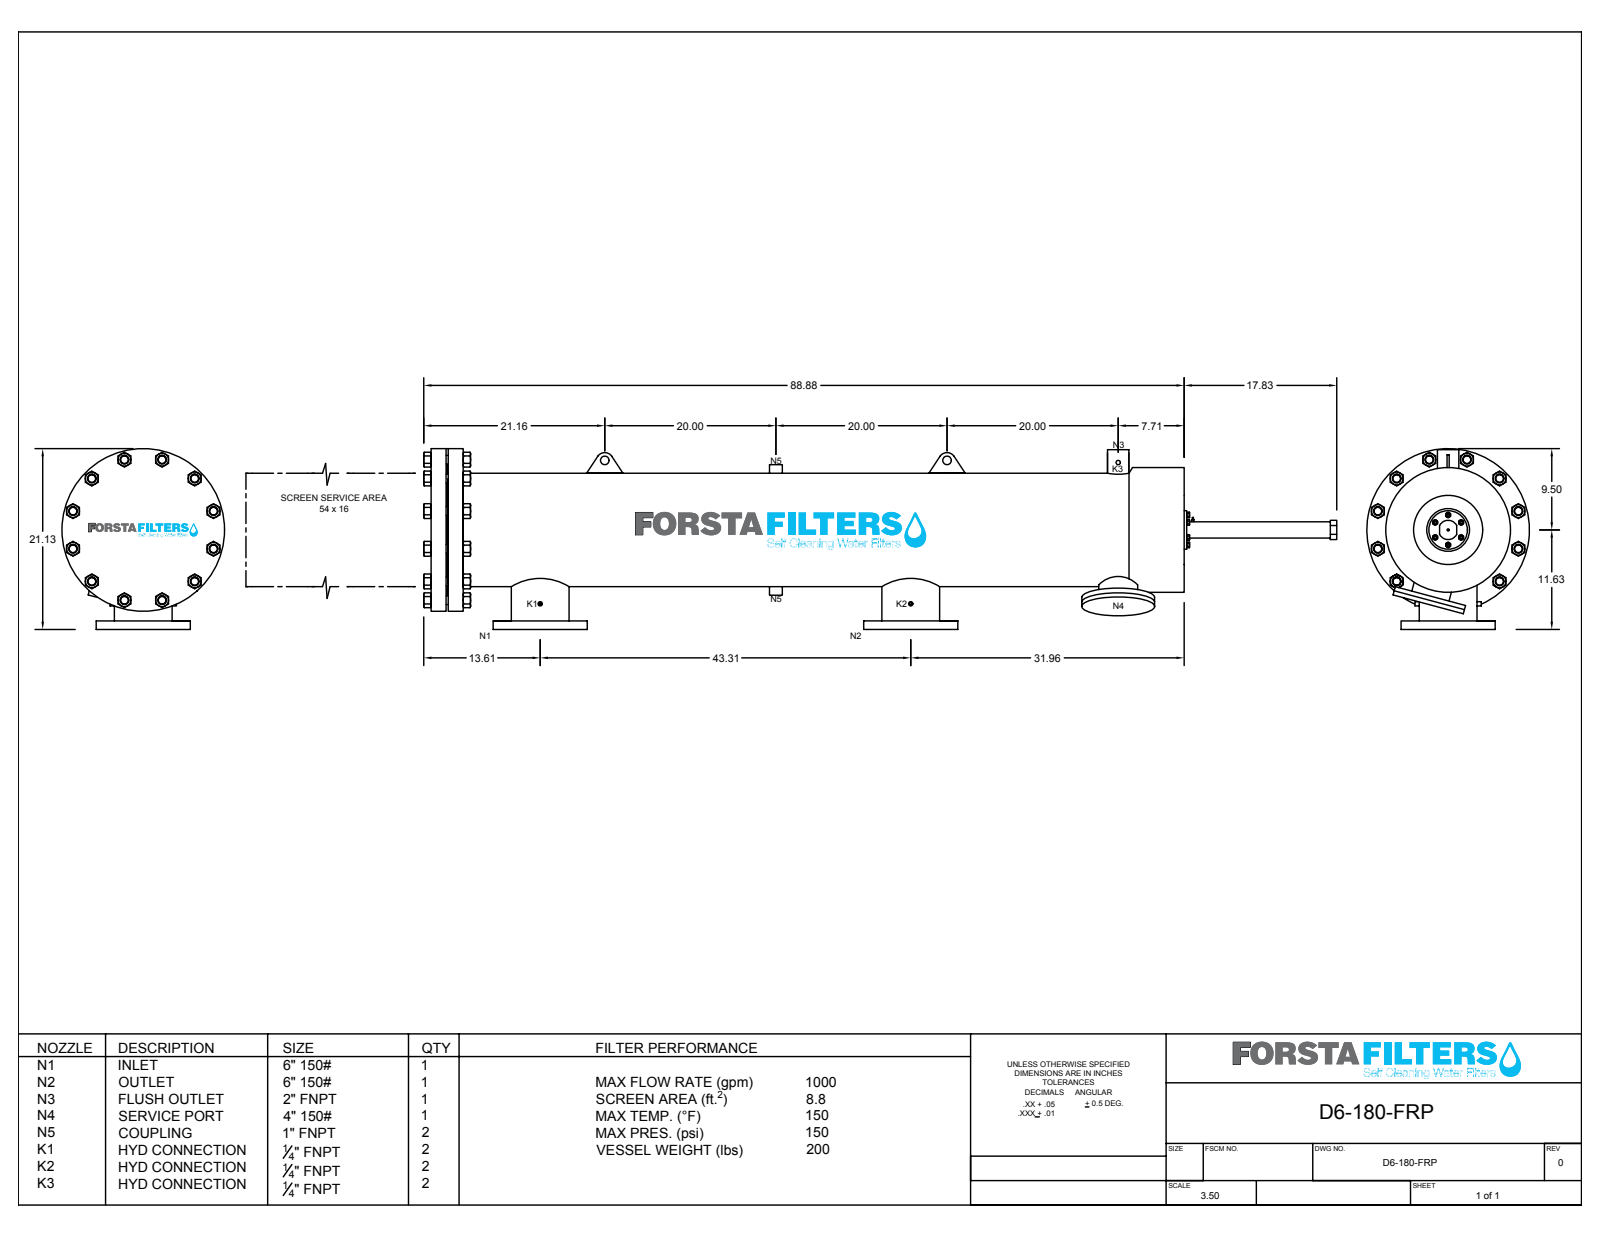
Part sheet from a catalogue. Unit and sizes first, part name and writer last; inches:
Units: inches
Overall size (bounding box): 107.21 × 21.13 × 19
Round holes (diameter × count): ⌀0.75 ×16, ⌀0.88 ×16, ⌀1 ×15, ⌀0.375 ×5, ⌀0.25 ×4, ⌀4 ×2, ⌀6 ×2, ⌀0.375 ×1, ⌀1.506 ×1, ⌀12.86 ×1, ⌀14.187 ×1
Round bosses / shafts (diameter × count): ⌀0.644 ×3, ⌀11 ×2, ⌀9 ×2, ⌀6.394 ×2, ⌀4.394 ×2, ⌀19 ×1, ⌀14.581 ×1, ⌀4.501 ×1
Partial cylindrical surfaces — rounded edges, fillets, slot ends (radius × count): R1 ×2, R1.125 ×1
Main face-to-face distances: 2, 0.5, 1, 88.707, 86.707, 88.51, 86.51, 0.197, 3.75, 1.75
Hole centre spacings: 2.87, 3.75, 5.303, 6.929, 3.636, 8.5, 6.718, 8.778
Volume: 1 853 in³ · Surface area: 10 729 in²
Bodies: 19 solids, 662 faces (296 planar, 342 cylindrical, 24 other)
Part name (STEP PRODUCT): D6-FRP-180
STEP written by: SolidWorks 2018 (CONFIG_CONTROL_DESIGN)
